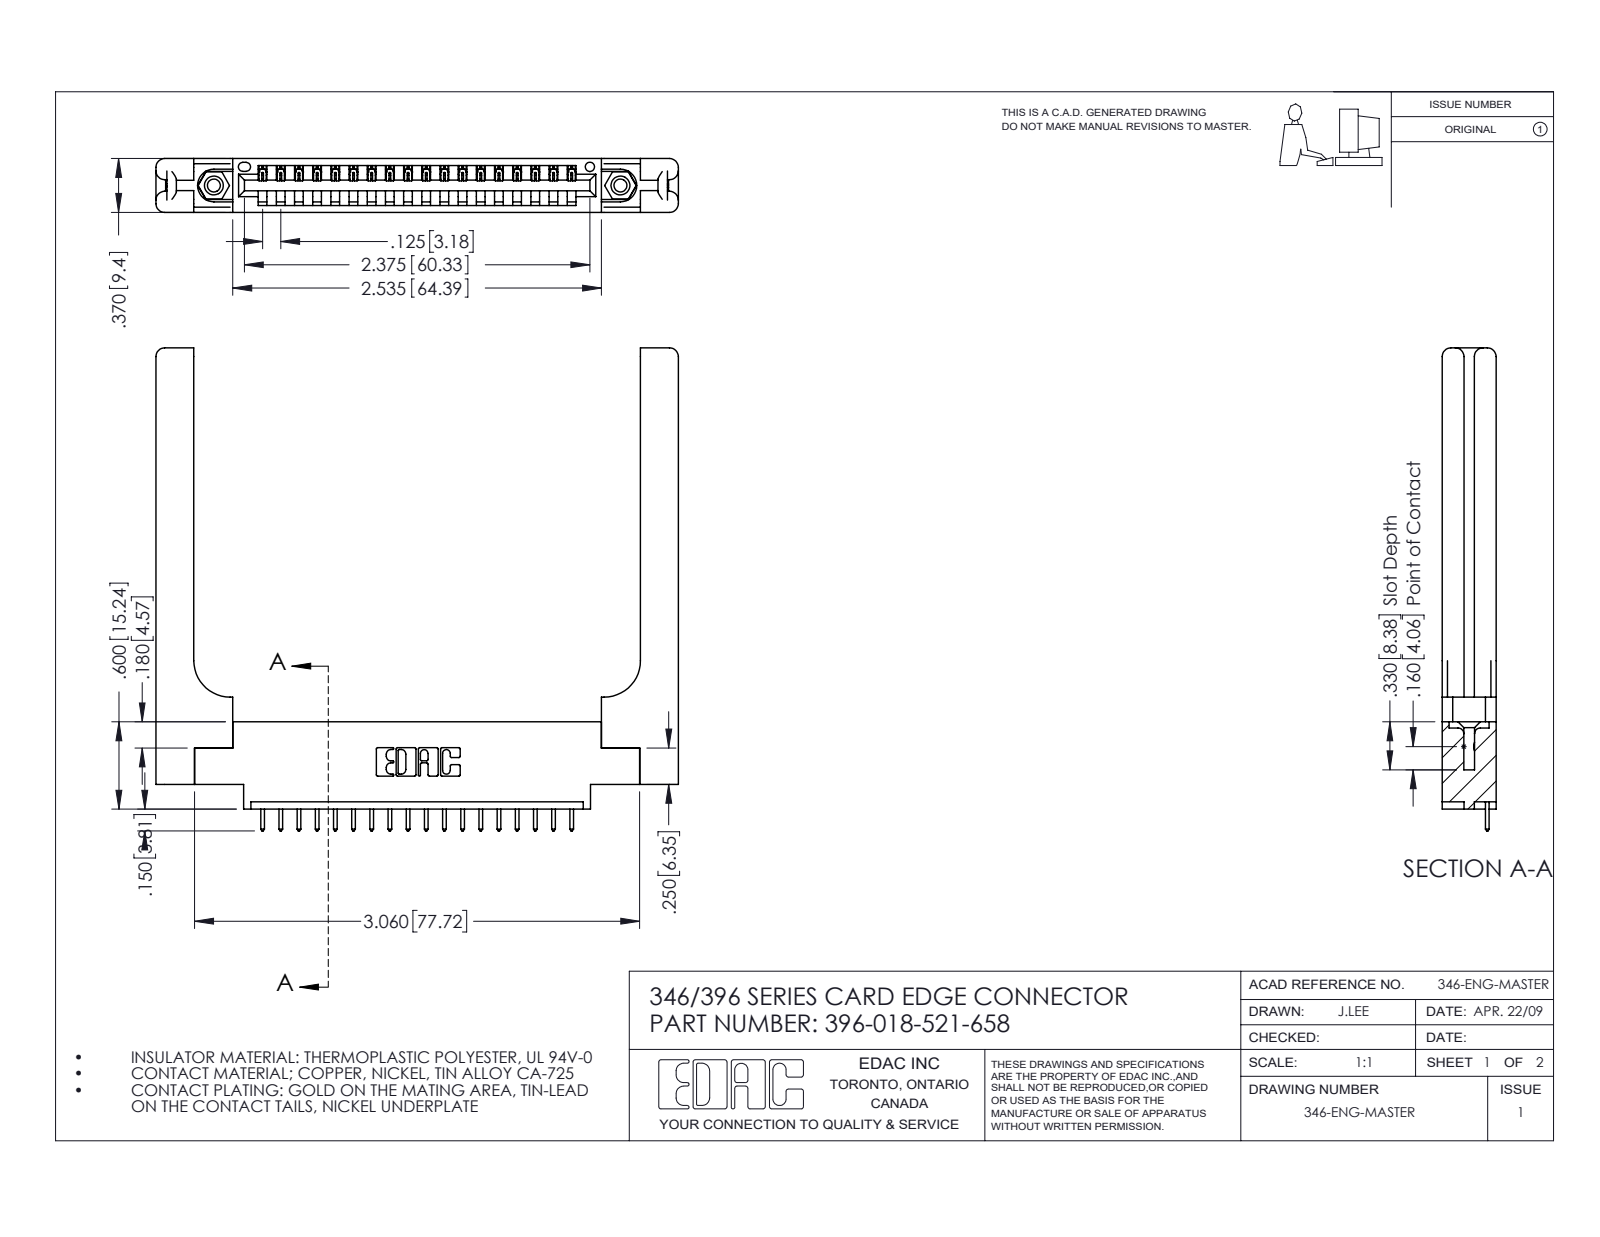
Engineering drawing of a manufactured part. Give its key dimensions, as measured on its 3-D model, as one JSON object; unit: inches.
{"part_name": "345-292-001_345-293-121; 396-018-521-658; 346-220-058_345-220-058; 346 Part_0.170 Offset - 0.156 Dia-TH (+1 more)", "step_written_by": "SolidWorks 2016 (CONFIG_CONTROL_DESIGN)", "units": "inches", "bodies": {"solids": 23, "faces": 1426, "planar": 948, "cylindrical": 418, "other": 60}, "overall_size": [3.591, 3.32, 0.37], "volume_in3": 0.969, "surface_area_in2": 23.74, "round_holes": [[0.089, 2], [0.125, 2], [0.156, 2], [0.064, 1]], "round_bosses_or_shafts": [[0.155, 2]], "partial_cylinders_radius": [[0.006, 36], [0.01, 36], [0.01, 22], [0.06, 16], [0.007, 6], [0.031, 6], [0.026, 3], [0.03, 2]], "face_to_face_distances": [0.37, 0.15, 0.072, 0.148, 0.048, 0.322, 0.25, 0.102, 0.22, 0.173], "hole_center_spacings": [0.246, 2.588, 2.795]}
